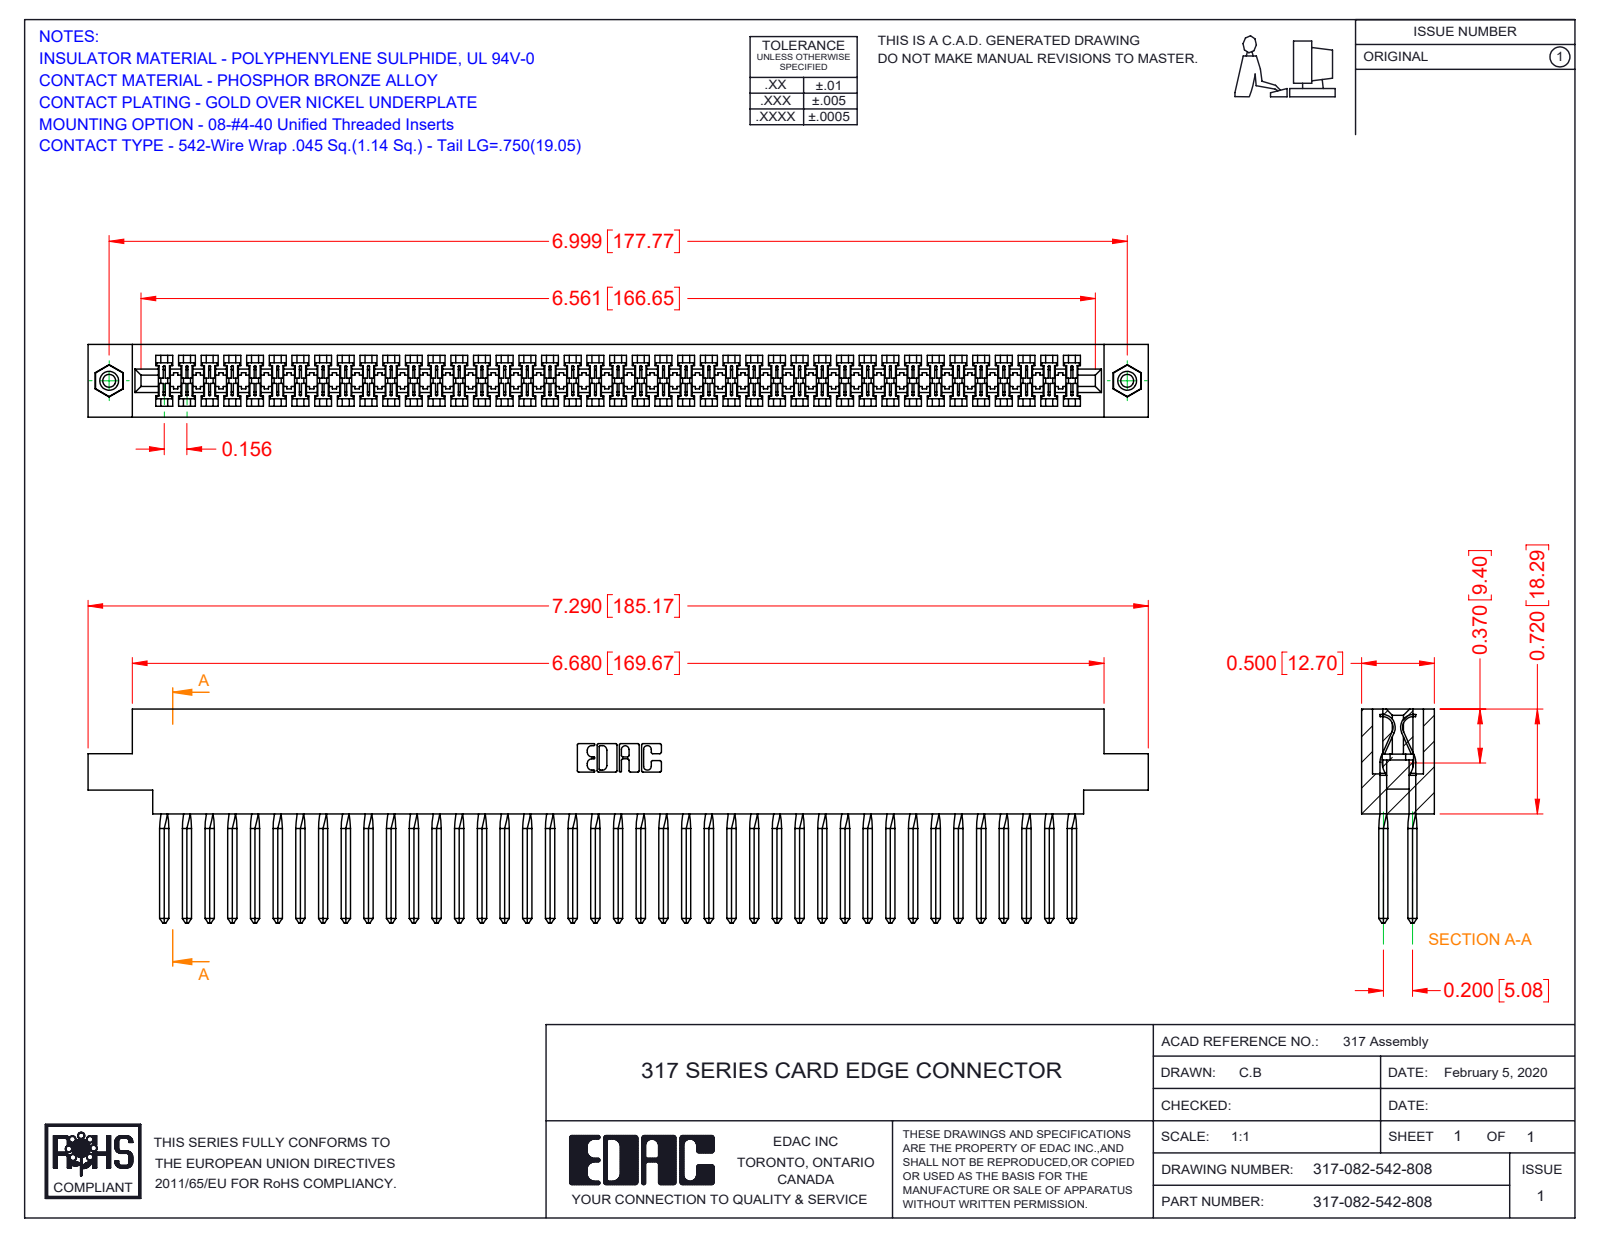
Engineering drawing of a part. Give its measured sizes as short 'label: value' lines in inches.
name: 317-082-542-808; 317-290-003_542; 345-250-001_345-250-003-102; 317 Part_.156 Dia - TI
written by: SolidWorks 2016 (CONFIG_CONTROL_DESIGN)
unit: in
bodies: 85 solids, 4836 faces (3862 planar, 630 cylindrical, 344 other)
size: 7.29 × 1.47 × 0.5
volume: 1.848 in³; area: 65.26 in²
holes: 2× ⌀0.089, 2× ⌀0.125, 2× ⌀0.156
bosses: 2× ⌀0.155
rounds: 164× R0.006, 22× R0.01, 6× R0.007, 6× R0.031, 3× R0.026, 2× R0.074, 2× R0.089, 2× R0.1
face distances: 0.5, 0.075, 0.425, 0.35, 0.2, 0.046, 0.128, 0.372, 0.052, 0.297
hole spacings: 6.999
